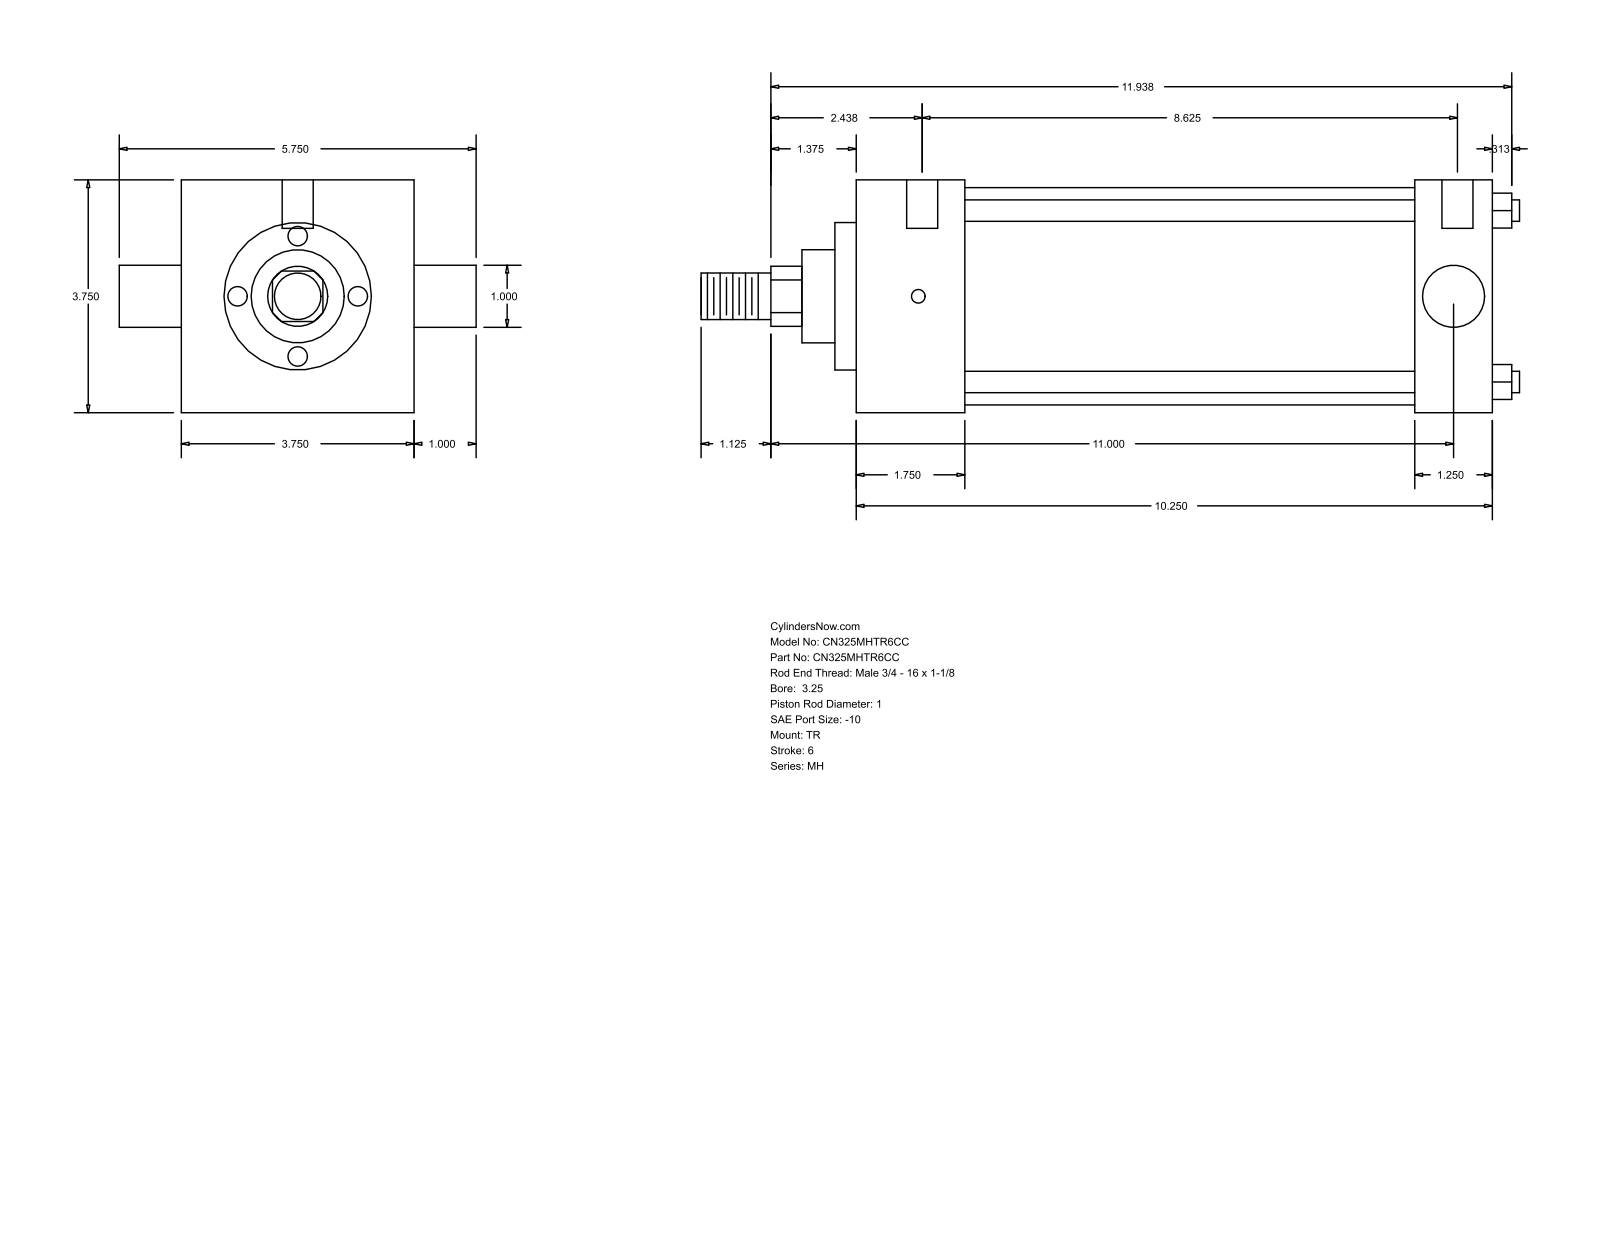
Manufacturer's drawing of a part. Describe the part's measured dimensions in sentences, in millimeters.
The part is named "MH_TR__0325_1". Its 3-D file was written by "GSSL Pune (CONFIG_CONTROL_DESIGN)". It is 0 solids with 86 faces: 61 planar, 25 cylindrical and 0 other. Overall it measures 334.96 by 146.05 by 95.25 millimeters. Round holes: 3 of diameter 5.56, 2 of diameter 12.7. Round bosses or shafts: 4 of diameter 8.76, 2 of diameter 25.4, 1 of diameter 88.9, 1 of diameter 60.33, 1 of diameter 38.1, 1 of diameter 19.05. Partial cylindrical surfaces (rounded edges, fillets, slot ends): 1 of radius 12.29. The main face-to-face distances are 95.24, 260.35, 44.46, 228.6, 184.14, 215.89, 31.75, 8.73, 53.19, 237.33. The hole center spacings are 1.58, 4.76, 219.08, 220.66, 223.84, 225.42.
